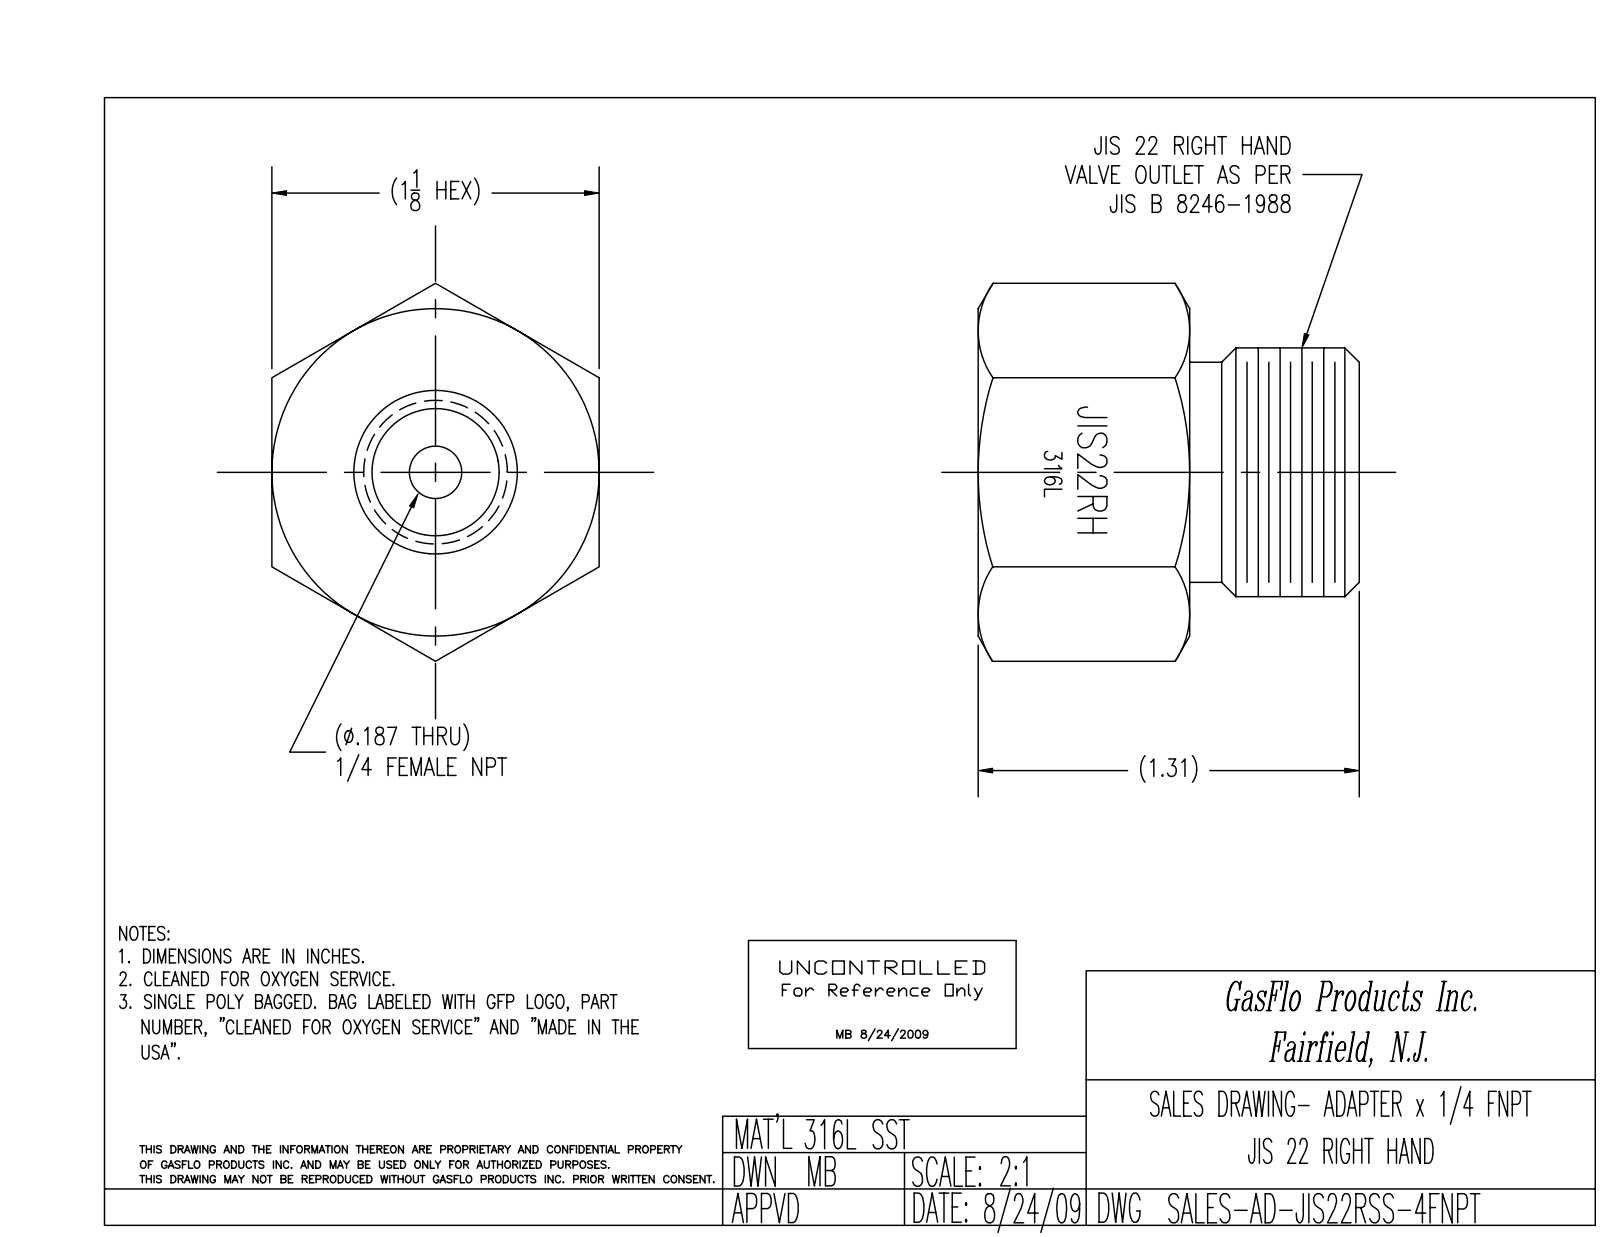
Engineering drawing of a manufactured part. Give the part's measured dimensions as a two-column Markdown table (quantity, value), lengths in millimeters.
| quantity | value |
| --- | --- |
| part name | AD-JIS22RSS-4FNPT |
| STEP written by | SolidWorks 2018 (CONFIG_CONTROL_DESIGN) |
| units | millimeters |
| bodies | 1 solid, 209 faces (88 planar, 23 cylindrical, 98 other) |
| overall size | 33.3 × 33 × 28.6 |
| volume | 14 400 mm³ |
| surface area | 6 126 mm² |
| round holes (diameter × count) | 4.7 × 1, 10.7 × 1, 12.5 × 1 |
| round bosses / shafts (diameter × count) | 21.8 × 1, 19.2 × 1 |
| main face-to-face distances | 28.6, 18.5, 33.3, 14.8, 23.1, 4.6, 10.2, 28.4, 5.1, 8 |
